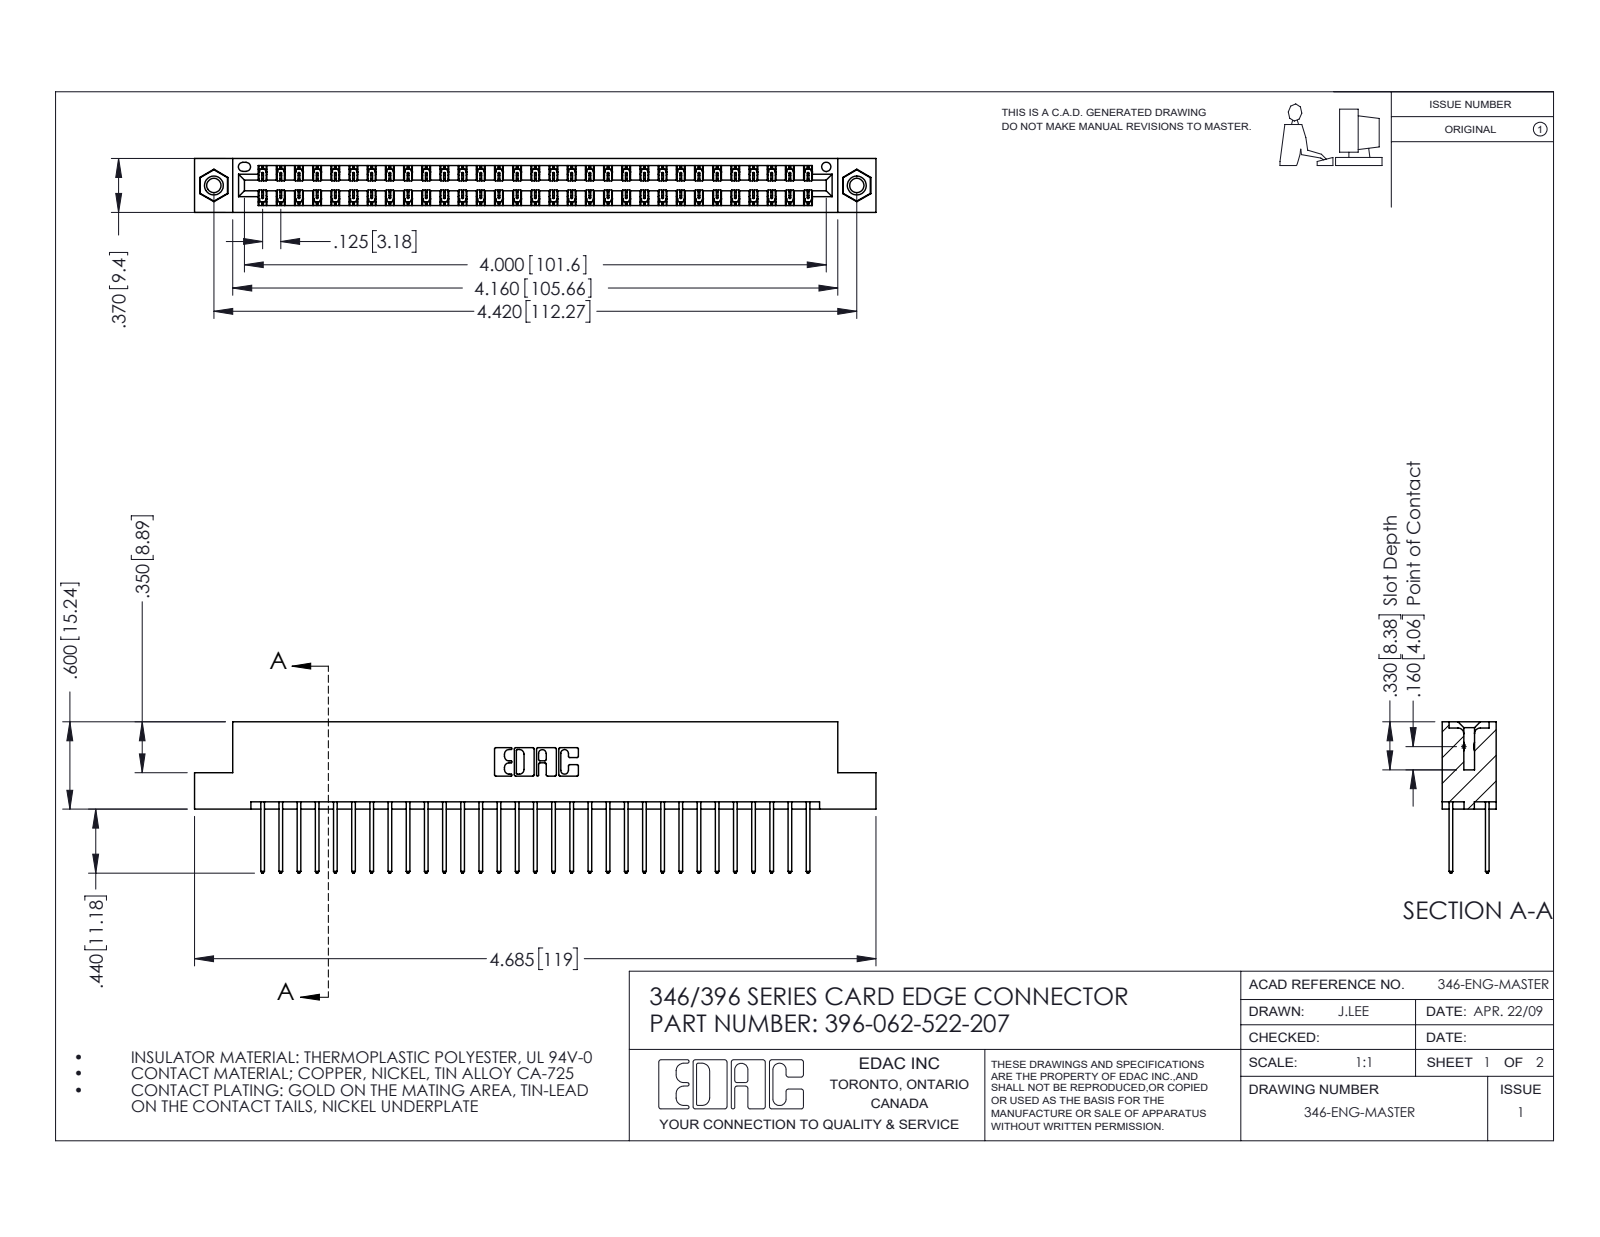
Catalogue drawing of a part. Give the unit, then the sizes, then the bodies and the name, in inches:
Units: inches
Overall size (bounding box): 4.685 × 1.04 × 0.37
Round holes (diameter × count): ⌀0.098 ×2, ⌀0.125 ×2, ⌀0.156 ×2, ⌀0.064 ×1
Round bosses / shafts (diameter × count): ⌀0.155 ×2
Partial cylindrical surfaces — rounded edges, fillets, slot ends (radius × count): R0.006 ×93, R0.01 ×62, R0.01 ×22, R0.007 ×6, R0.031 ×6, R0.026 ×3, R0.014 ×2, R0.022 ×2
Main face-to-face distances: 0.048, 0.322, 0.25, 0.37, 0.072, 0.298, 0.025, 0.275, 0.148, 0.222
Hole centre spacings: 0.246, 4.212, 4.42
Volume: 0.712 in³ · Surface area: 25.78 in²
Bodies: 65 solids, 3406 faces (2278 planar, 1112 cylindrical, 16 other)
Part name (STEP PRODUCT): 396-062-522-207; 345-250-001_345-250-005-103; 345-292-001_345-293-122; 346 Part_Flush Mounting Lugs - 0.156 Dia-TI
STEP written by: SolidWorks 2016 (CONFIG_CONTROL_DESIGN)
